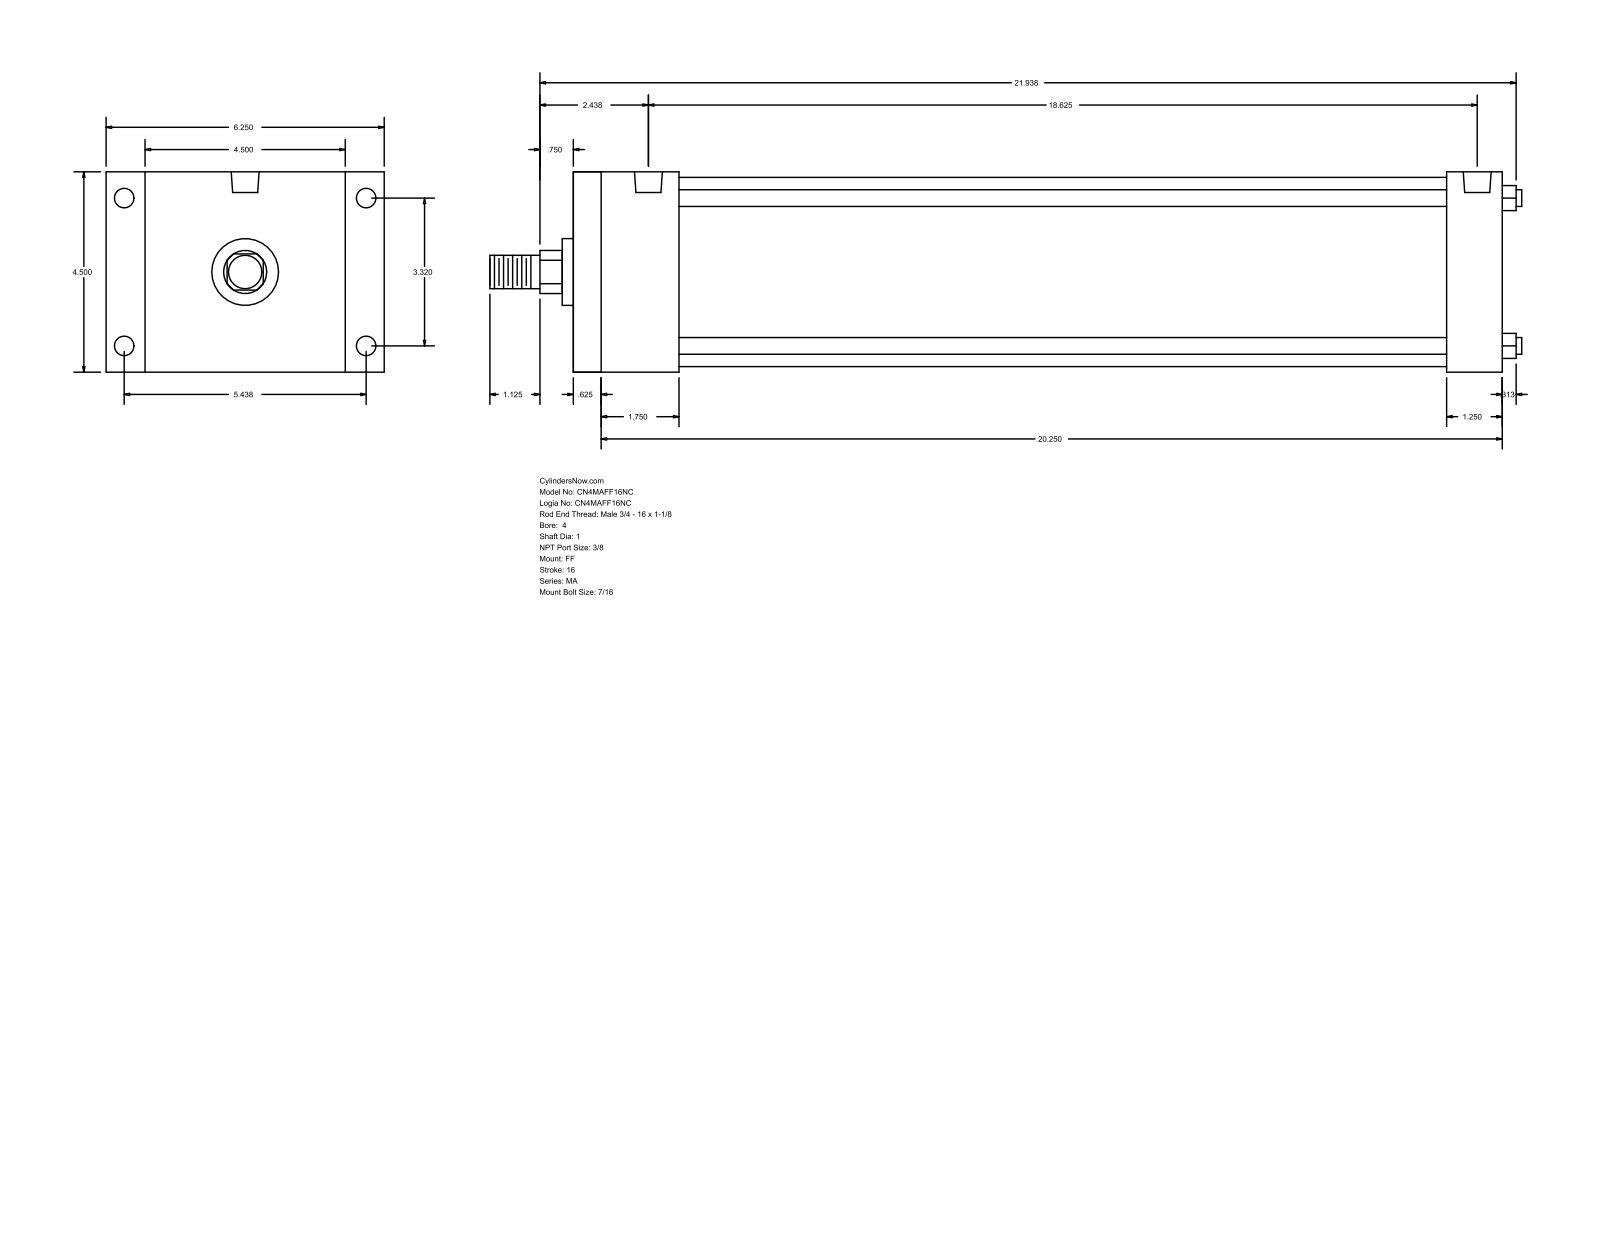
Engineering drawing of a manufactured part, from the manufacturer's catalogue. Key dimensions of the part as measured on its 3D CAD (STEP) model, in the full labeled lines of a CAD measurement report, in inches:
Part name (STEP PRODUCT): MA_FF__0400_1
STEP written by: GSSL Pune (CONFIG_CONTROL_DESIGN)
Units: inches
Bodies: 0 solids, 92 faces (64 planar, 28 cylindrical, 0 other)
Overall size (bounding box): 23.187 × 6.25 × 4.5
Round holes (diameter × count): ⌀0.437 ×8, ⌀0.627 ×2
Round bosses / shafts (diameter × count): ⌀0.375 ×4, ⌀4.25 ×1, ⌀1.5 ×1, ⌀1 ×1, ⌀0.75 ×1
Partial cylindrical surfaces — rounded edges, fillets, slot ends (radius × count): R0.484 ×1
Main face-to-face distances: 4.5, 20.875, 0.625, 20.25, 0.875, 5.375, 19.625, 19, 1.25, 2.375
Hole centre spacings: 0.187, 3.32, 5.438, 6.371, 18.25, 18.438, 18.625
